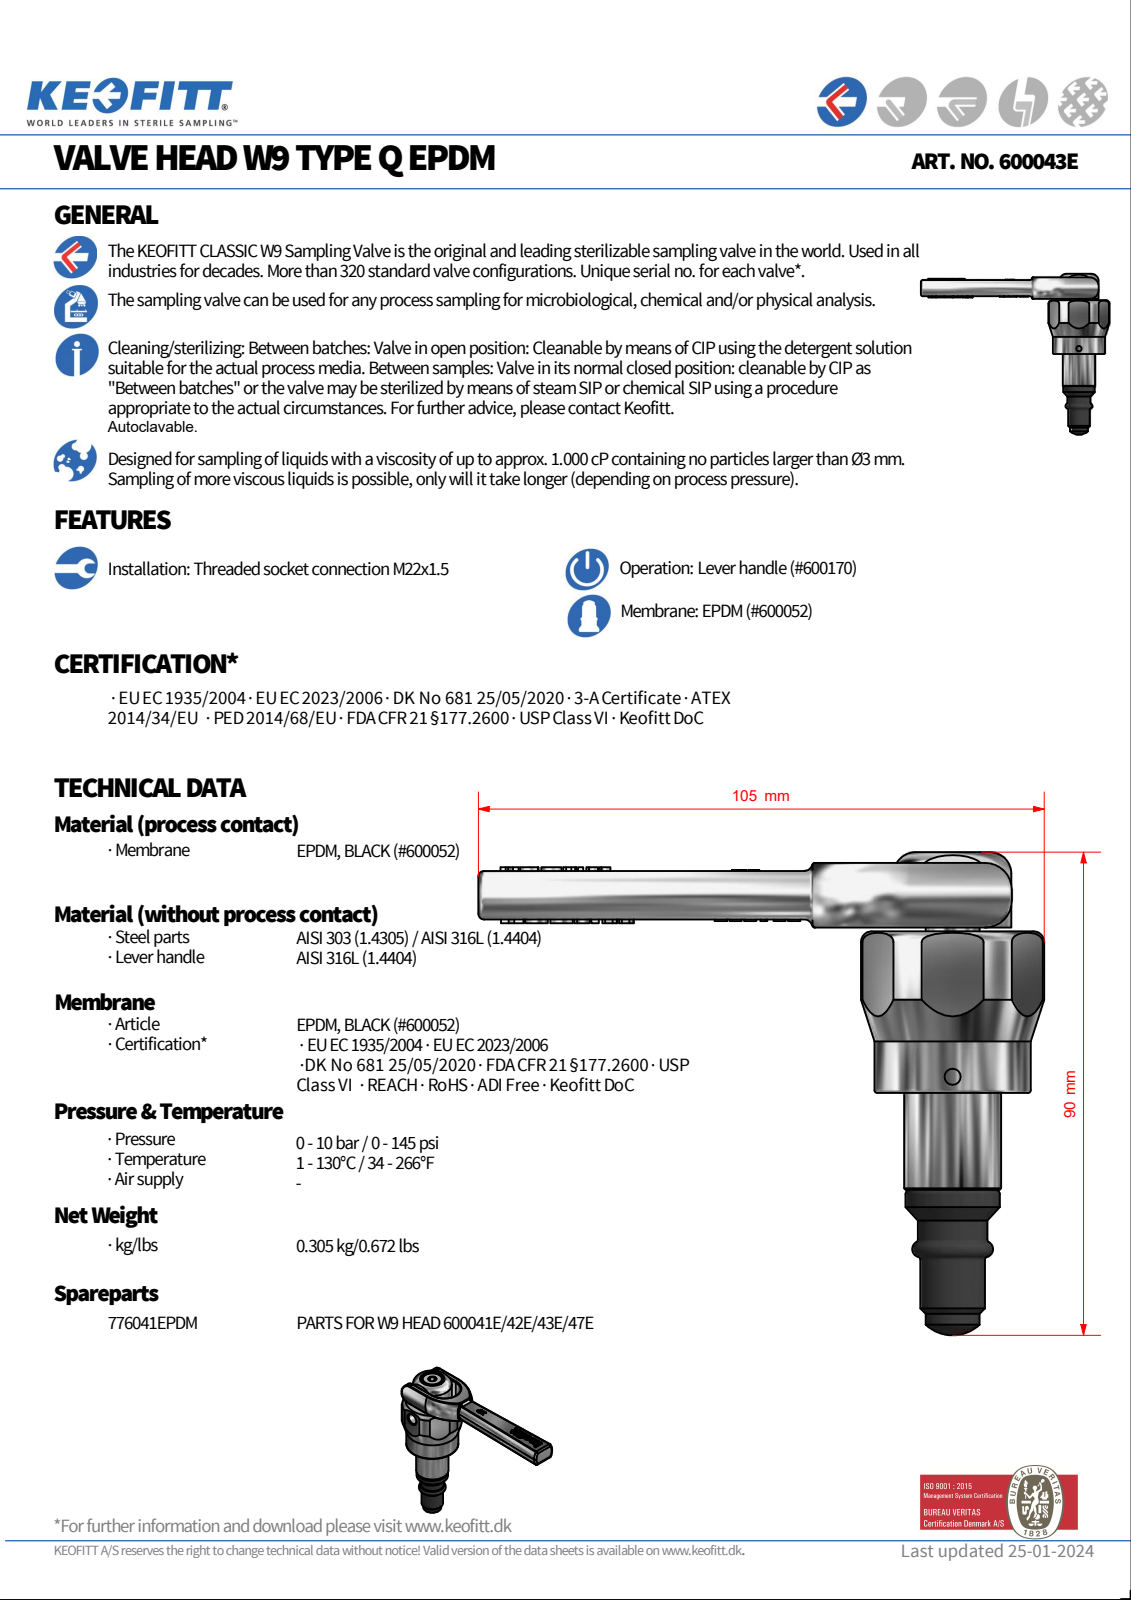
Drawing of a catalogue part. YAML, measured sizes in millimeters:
step_written_by: "Autodesk Inventor 2008 (AUTOMOTIVE_DESIGN)"
units: millimeters
bodies: {solids: 1, faces: 540, planar: 225, cylindrical: 54, other: 261}
overall_size: [104.83, 87.9, 32]
volume: 44907
surface_area: 13270
round_holes:
  - {diameter: 2.5, count: 1}
  - {diameter: 3.05, count: 1}
  - {diameter: 6, count: 1}
  - {diameter: 6.05, count: 1}
  - {diameter: 11.5, count: 1}
  - {diameter: 23.4, count: 1}
round_bosses_or_shafts:
  - {diameter: 29, count: 1}
  - {diameter: 18, count: 1}
  - {diameter: 17.5, count: 1}
  - {diameter: 12.9, count: 1}
  - {diameter: 12, count: 1}
  - {diameter: 10, count: 1}
  - {diameter: 3, count: 1}
partial_cylinders:
  - {radius: 0.5, count: 10}
  - {radius: 1.5, count: 4}
  - {radius: 1, count: 2}
  - {radius: 5, count: 2}
  - {radius: 3, count: 1}
  - {radius: 5.4, count: 1}
  - {radius: 9.1, count: 1}
  - {radius: 11, count: 1}
face_to_face_distances: [32, 9, 1.5, 10.5, 0.85, 9.85, 11.35, 30, 30.85, 39.85]
hole_center_spacings: [2, 8.39, 10.38, 22, 24, 32.36]
